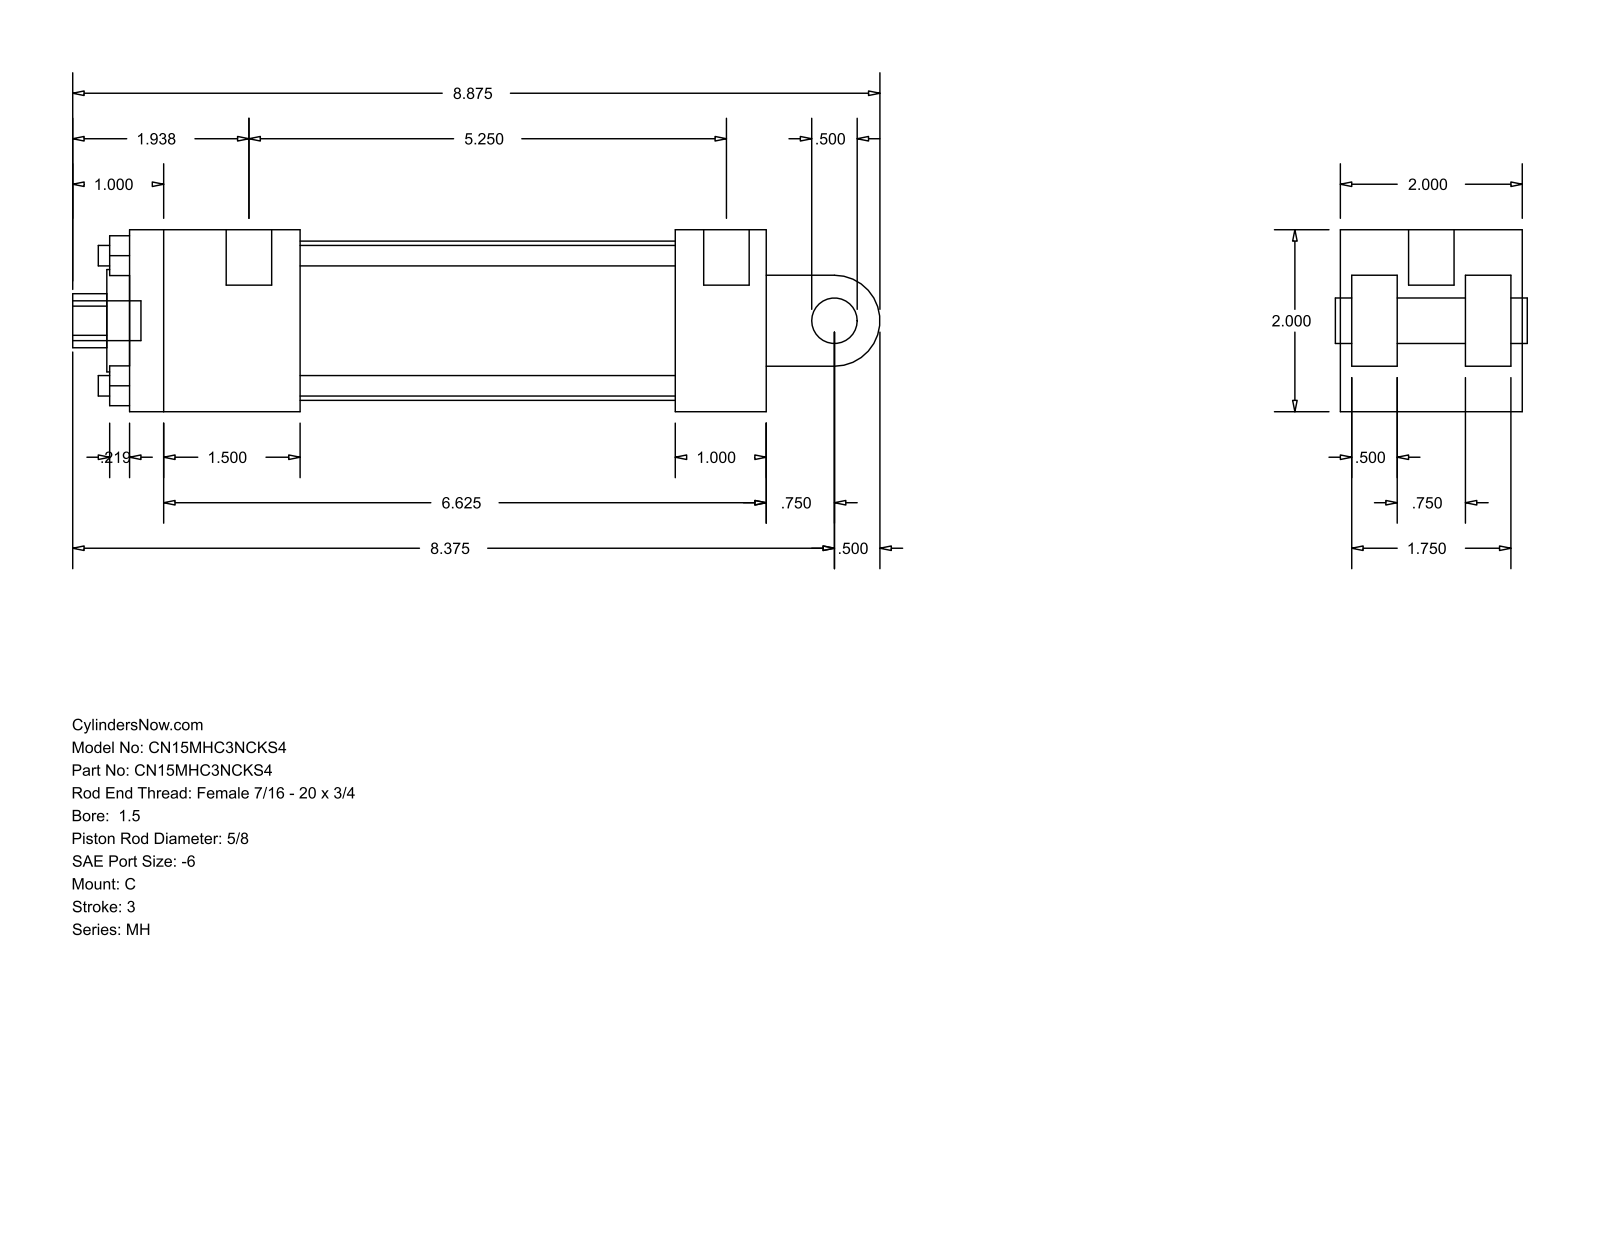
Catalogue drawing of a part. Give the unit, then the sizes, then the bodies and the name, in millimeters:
Units: millimetres
Overall size (bounding box): 225.43 × 50.8 × 50.8
Round holes (diameter × count): ⌀5.71 ×4, ⌀5.56 ×2, ⌀12.7 ×1, ⌀15.88 ×1, ⌀28.57 ×1, ⌀44.45 ×1
Round bosses / shafts (diameter × count): ⌀12.7 ×2, ⌀5.56 ×2, ⌀11.11 ×1
Partial cylindrical surfaces — rounded edges, fillets, slot ends (radius × count): R7.54 ×1, R12.7 ×1
Main face-to-face distances: 50.8, 12.7, 177.8, 25.4, 3.17, 47.63, 15.87, 34.93, 31.76, 38.1
Hole centre spacings: 25.68, 36.32, 51.36
Bodies: 0 solids, 99 faces (70 planar, 29 cylindrical, 0 other)
Part name (STEP PRODUCT): MH_C__0150_0.625
STEP written by: GSSL Pune (CONFIG_CONTROL_DESIGN)
